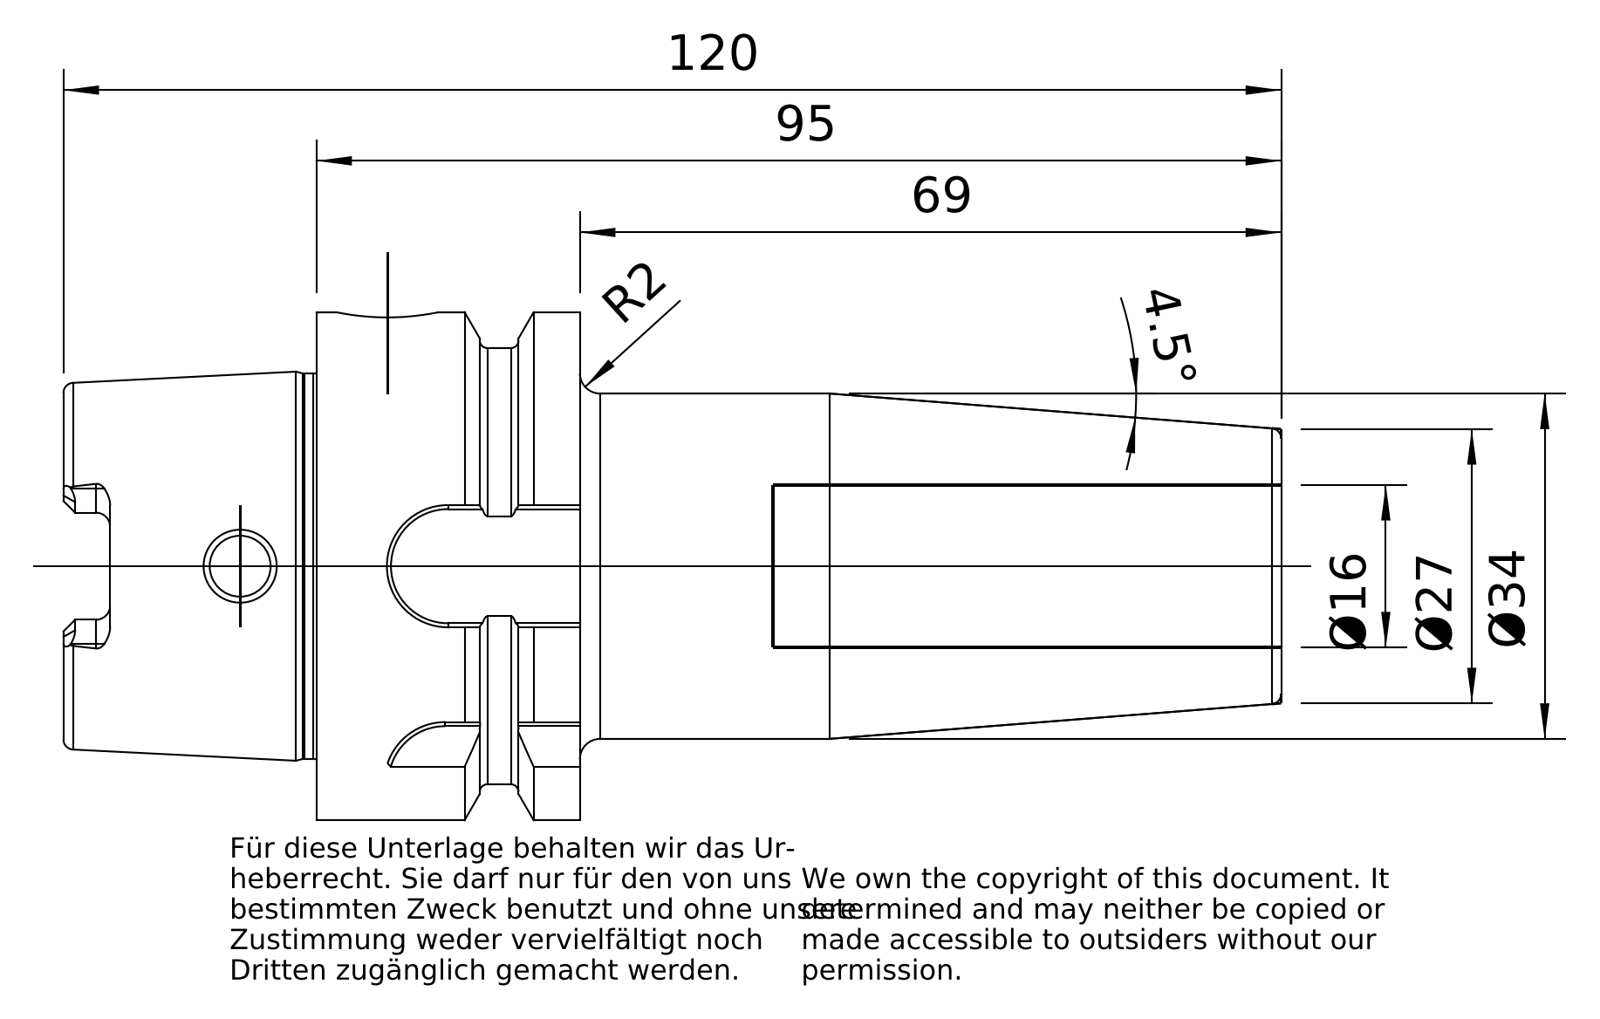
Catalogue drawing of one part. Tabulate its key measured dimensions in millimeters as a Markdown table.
| quantity | value |
| --- | --- |
| part name | A50-140-16 |
| STEP written by | PRO/ENGINEER BY PARAMETRIC TECHNOLOGY CORPORATION, 2010430 (CONFIG_CONTROL_DESIGN) |
| units | millimeters |
| bodies | 1 solid, 184 faces (63 planar, 49 cylindrical, 72 other) |
| overall size | 119.9 × 50 × 50 |
| volume | 93 843 mm³ |
| surface area | 24 267 mm² |
| round holes (diameter × count) | 6 × 1, 10 × 1, 14 × 1, 16 × 1, 16.32 × 1, 16.5 × 1, 26.04 × 1, 32.08 × 1 |
| round bosses / shafts (diameter × count) | 50 × 1, 42.95 × 1, 37.91 × 1, 34 × 1 |
| partial cylindrical surfaces (radius × count) | 1.4 × 6, 2.38 × 4, 6 × 3, 6.02 × 1 |
| main face-to-face distances | 25.95, 95, 69.05, 24.9, 50.85, 119.9, 34.85, 9.95, 16, 85.05 |
